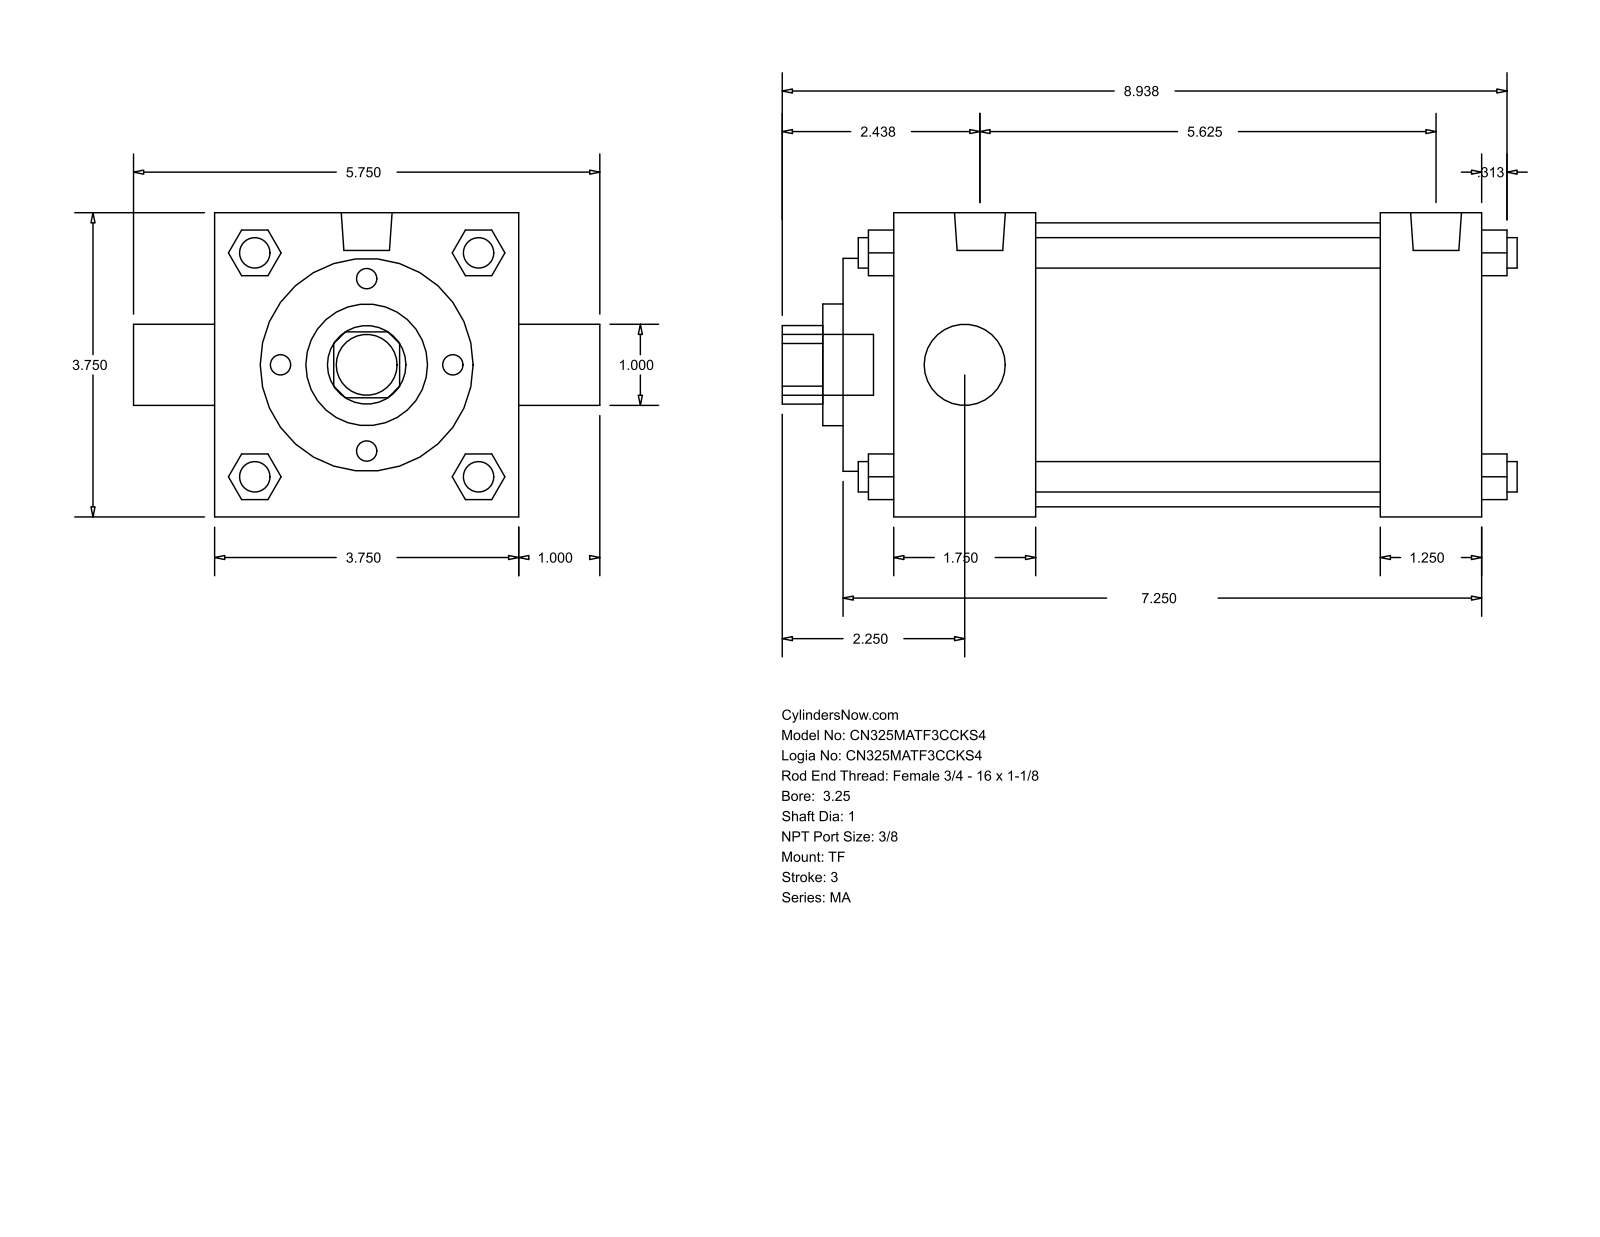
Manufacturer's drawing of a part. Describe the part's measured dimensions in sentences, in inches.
The part is named "MA_TF__0325_1". Its 3-D file was written by "GSSL Pune (CONFIG_CONTROL_DESIGN)". It is 0 solids with 122 faces: 93 planar, 29 cylindrical and 0 other. Overall it measures 9.063 by 5.75 by 3.75 inches. Round holes: 2 of diameter 1, 1 of diameter 1.5, 1 of diameter 2.625, 1 of diameter 3.5. Round bosses or shafts: 4 of diameter 0.375, 3 of diameter 0.437, 2 of diameter 0.627, 1 of diameter 0.75. Partial cylindrical surfaces (rounded edges, fillets, slot ends): 1 of radius 0.484. The main face-to-face distances are 3.75, 7.25, 7.875, 0.625, 1.75, 6, 4.25, 5.5, 1.25, 2.375.
